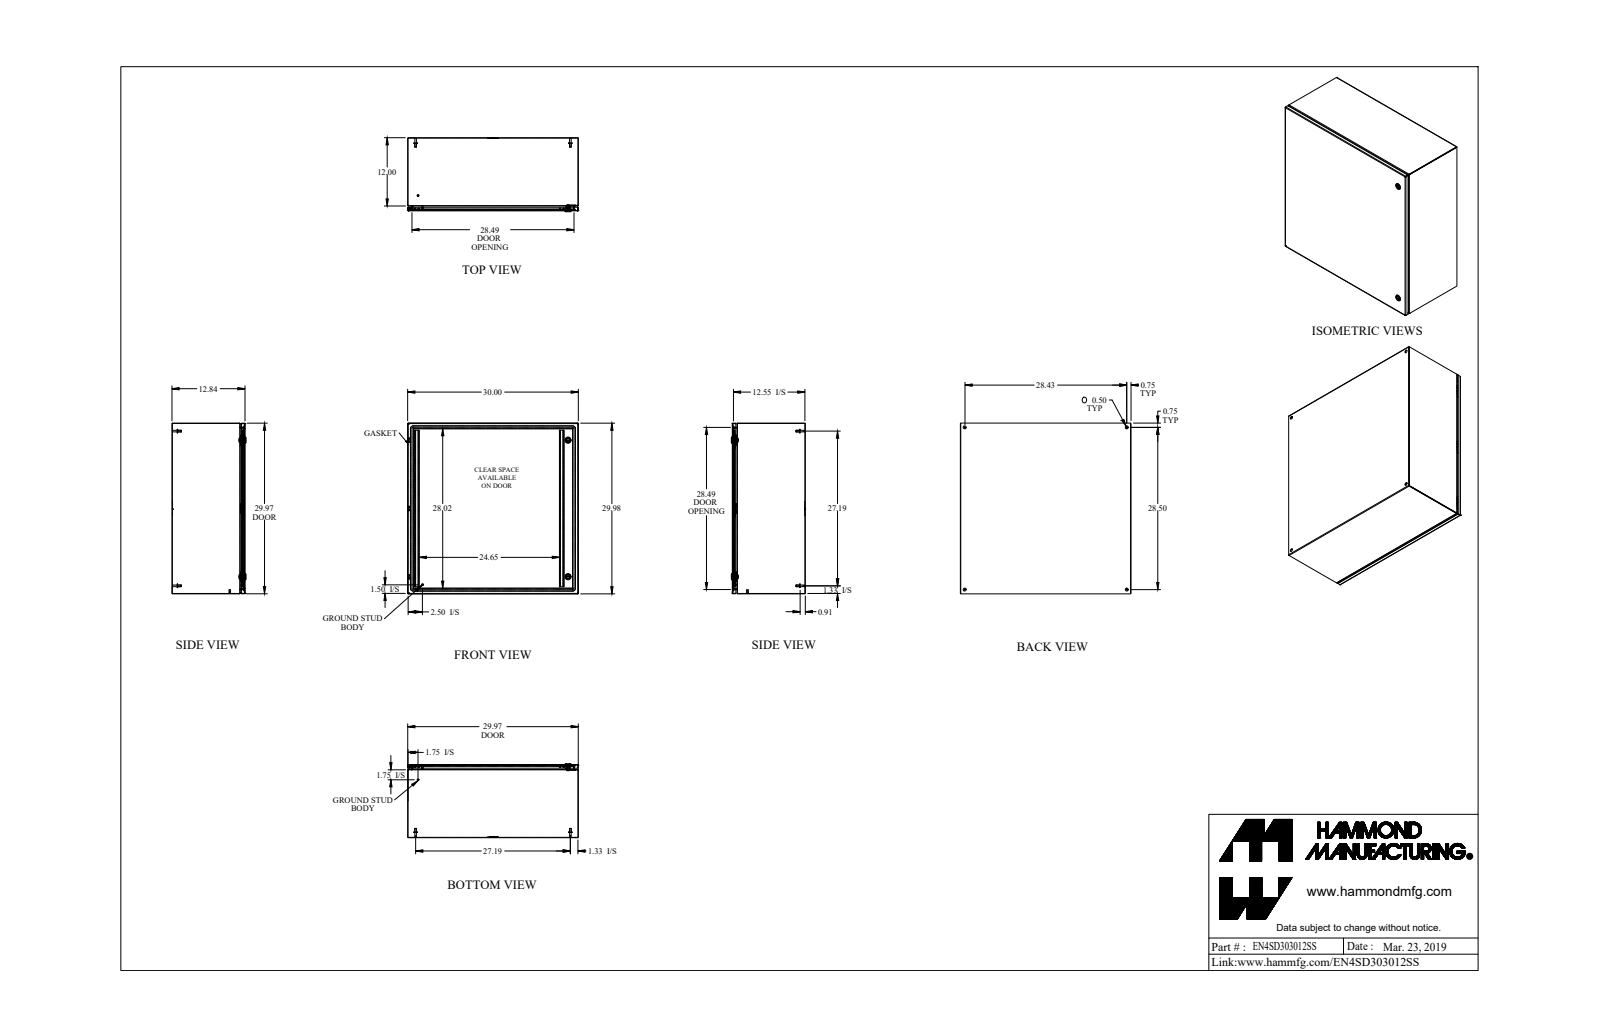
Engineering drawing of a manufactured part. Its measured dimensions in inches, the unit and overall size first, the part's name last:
Units: inches
Overall size (bounding box): 30 × 30 × 13.002
Round holes (diameter × count): ⌀0.5 ×6, ⌀0.197 ×2, ⌀0.387 ×2, ⌀0.63 ×2, ⌀0.768 ×2, ⌀0.172 ×1, ⌀0.24 ×1, ⌀0.242 ×1
Round bosses / shafts (diameter × count): ⌀0.313 ×6, ⌀0.625 ×4, ⌀0.275 ×4, ⌀1.1 ×2, ⌀0.785 ×2, ⌀0.625 ×2, ⌀0.525 ×2, ⌀0.25 ×2
Partial cylindrical surfaces — rounded edges, fillets, slot ends (radius × count): R0.108 ×22, R0.036 ×14, R0.01 ×12, R0.048 ×12, R0.312 ×12, R0.006 ×6, R0.062 ×6, R0.125 ×4
Main face-to-face distances: 0.072, 12.77, 29.928, 12.698, 12.842, 29.856, 30, 0.842, 11.928, 0.75
Hole centre spacings: 28.5, 27.531, 40.305, 2.487, 2.488, 24, 26.271, 26.272
Volume: 265.2 in³ · Surface area: 7 438 in²
Bodies: 35 solids, 876 faces (419 planar, 297 cylindrical, 160 other)
Part name (STEP PRODUCT): EN4SD303012SS
STEP written by: SolidWorks 2019 (AUTOMOTIVE_DESIGN)
